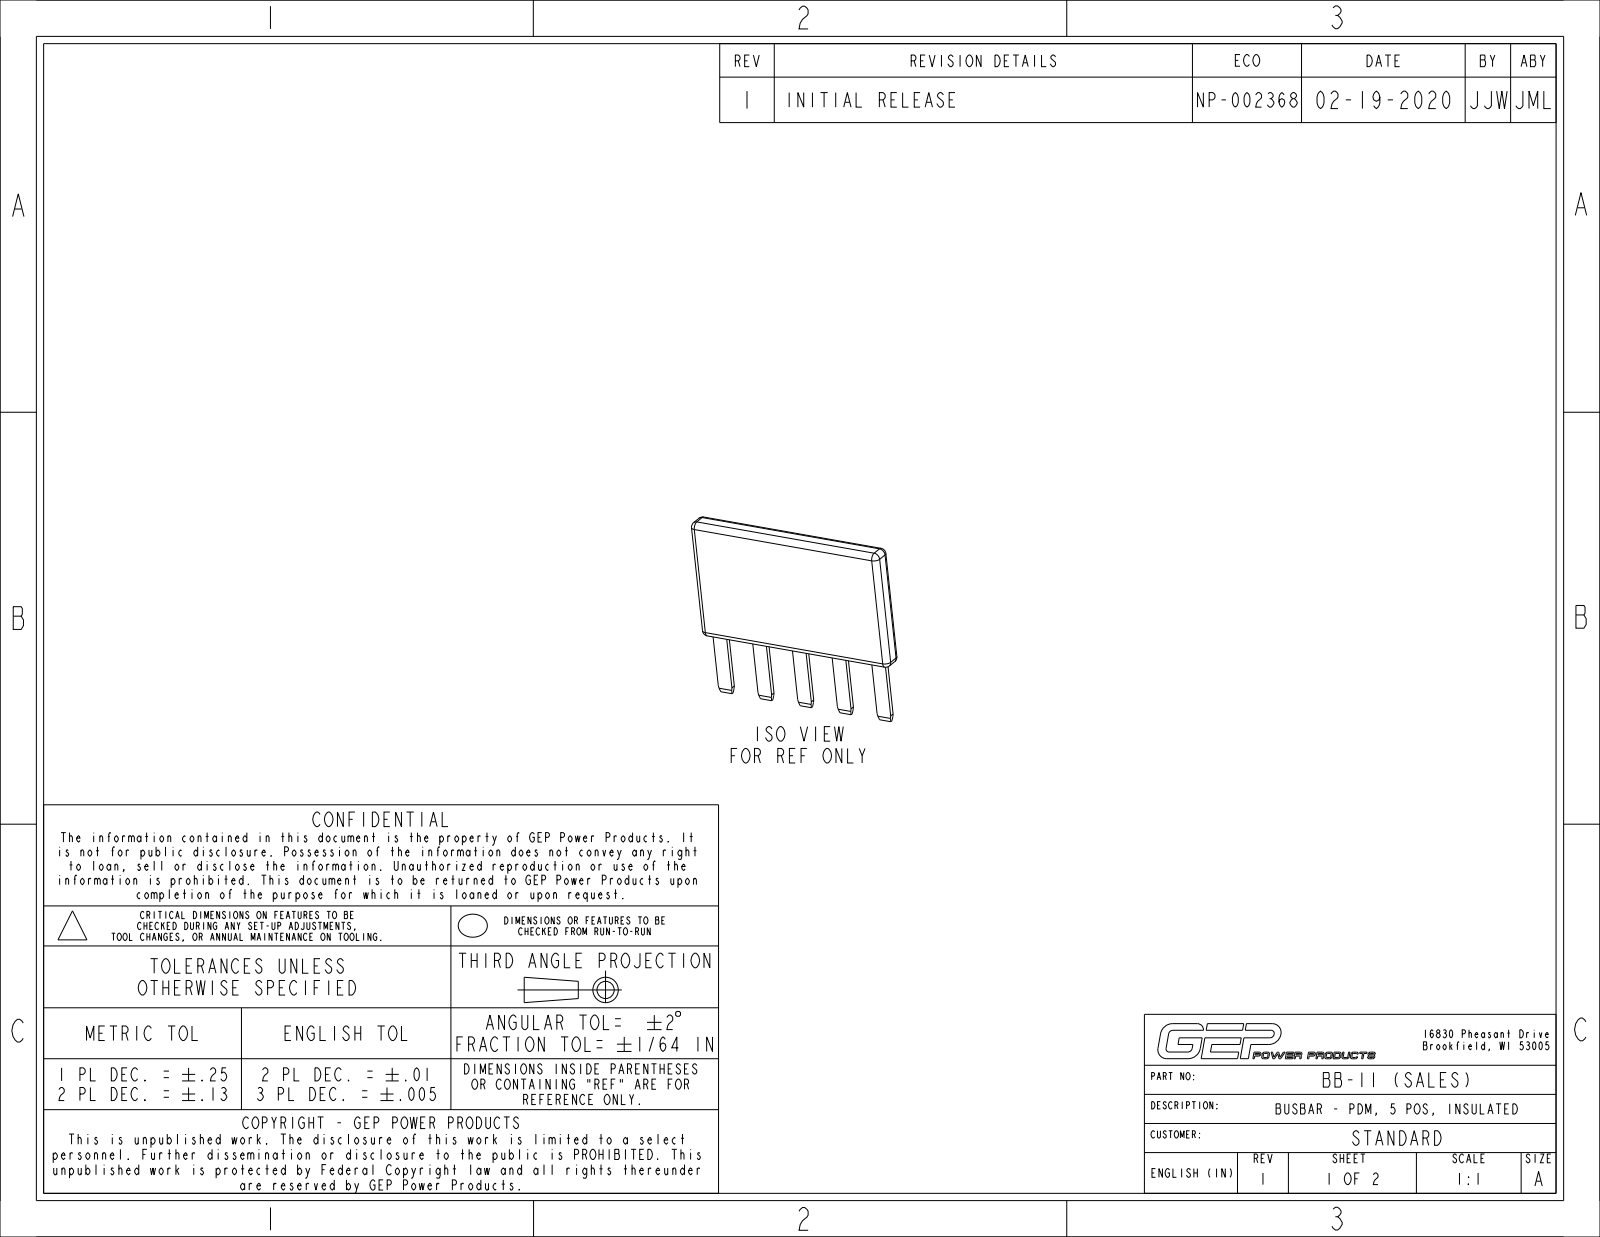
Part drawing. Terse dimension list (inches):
name: Q-BB-11_BAR_NCF; Q-BB-11_MOLD_NCF; Q-BB-11_NCF_ASM; Q-BB-11_SALES_NCF_ASM
written by: CREO PARAMETRIC BY PTC INC, 2017110 (CONFIG_CONTROL_DESIGN)
unit: in
bodies: 2 solids, 87 faces (67 planar, 12 cylindrical, 8 other)
size: 1.51 × 1.31 × 0.152
volume: 0.204 in³; area: 8.363 in²
rounds: 12× R0.04
face distances: 0.032, 0.06, 0.092, 0.152, 0.092, 0.06, 0.81, 0.32, 1.45, 0.75
